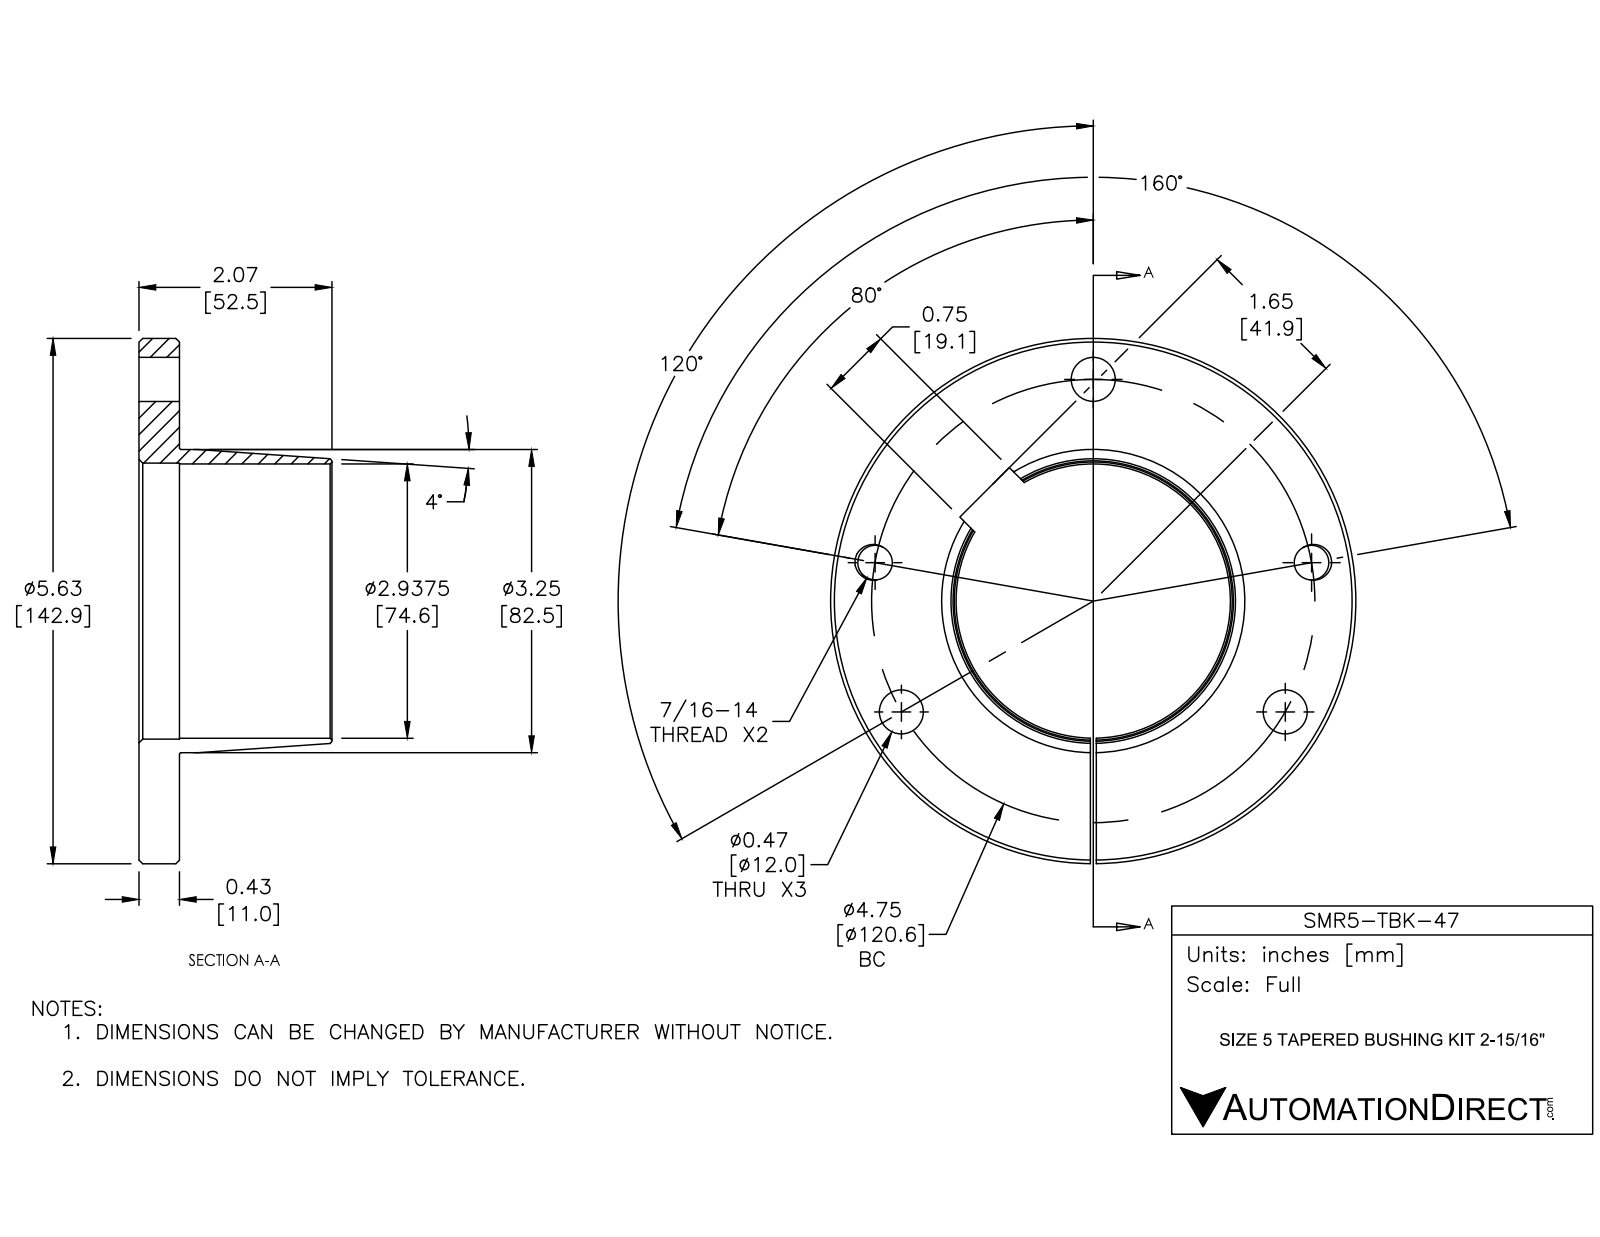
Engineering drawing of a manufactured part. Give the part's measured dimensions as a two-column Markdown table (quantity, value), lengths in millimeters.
| quantity | value |
| --- | --- |
| part name | SMR5-TBK-47 |
| STEP written by | SolidWorks 2016 (AUTOMOTIVE_DESIGN) |
| units | millimeters |
| bodies | 1 solid, 99 faces (11 planar, 67 cylindrical, 21 other) |
| overall size | 142.9 × 142.9 × 52.5 |
| volume | 146 000 mm³ |
| surface area | 50 210 mm² |
| round holes (diameter × count) | 12 × 3, 9.4 × 2, 10.9 × 2, 74.6 × 1, 75.1 × 1 |
| round bosses / shafts (diameter × count) | 142.9 × 1, 82.5 × 1 |
| main face-to-face distances | 11, 1.6, 19.1, 52.5, 41.5 |
| hole center spacings | 60.3, 104.4, 118.8, 41.2, 77.5 |
